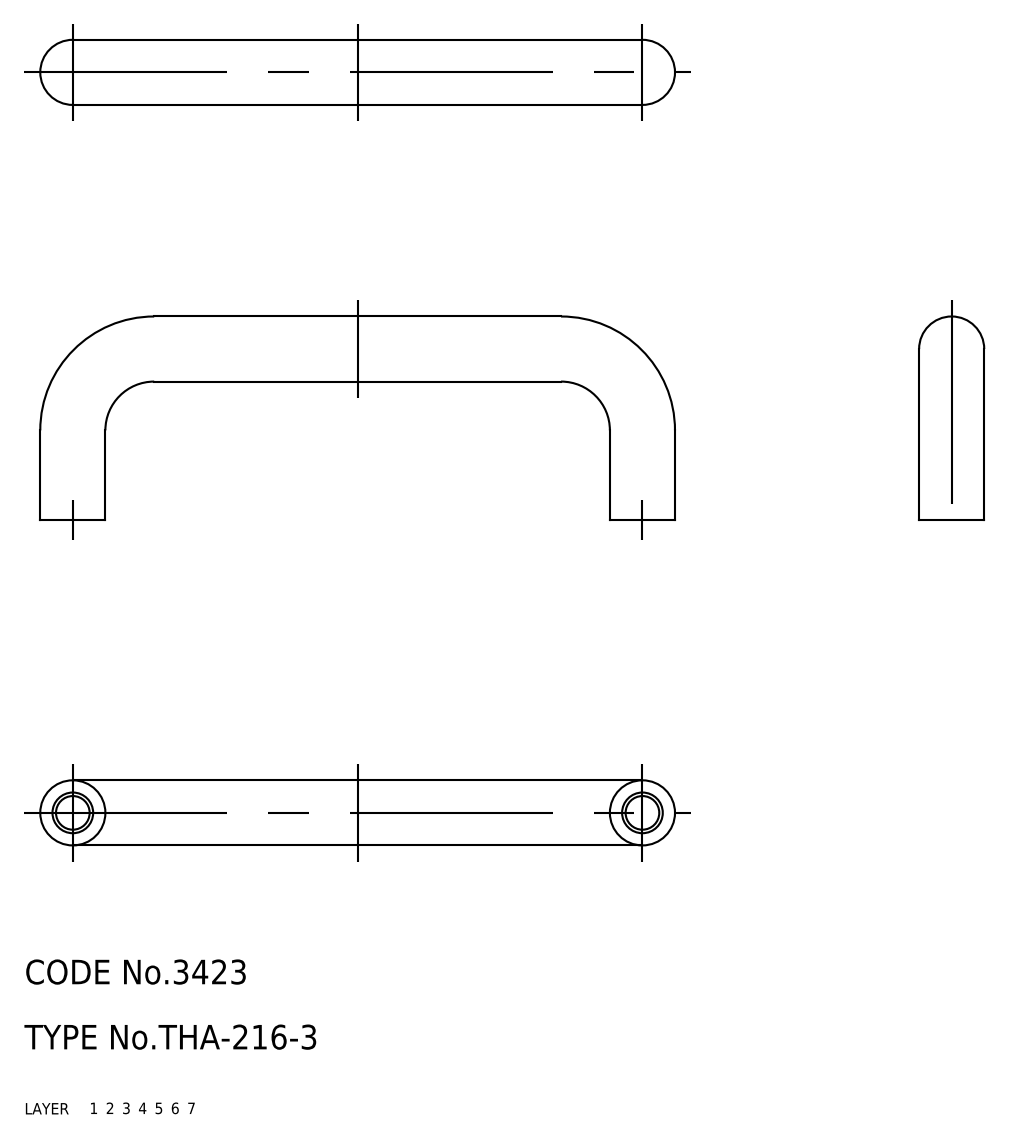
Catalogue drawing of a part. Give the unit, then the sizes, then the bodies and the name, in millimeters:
Units: millimetres
Overall size (bounding box): 78 × 25 × 8
Volume: 4 833 mm³ · Surface area: 3 016 mm²
Bodies: 1 solid, 18 faces (0 planar, 0 cylindrical, 18 other)
Part name (STEP PRODUCT): pull
STEP written by: CADfix (AUTOMOTIVE_DESIGN)
